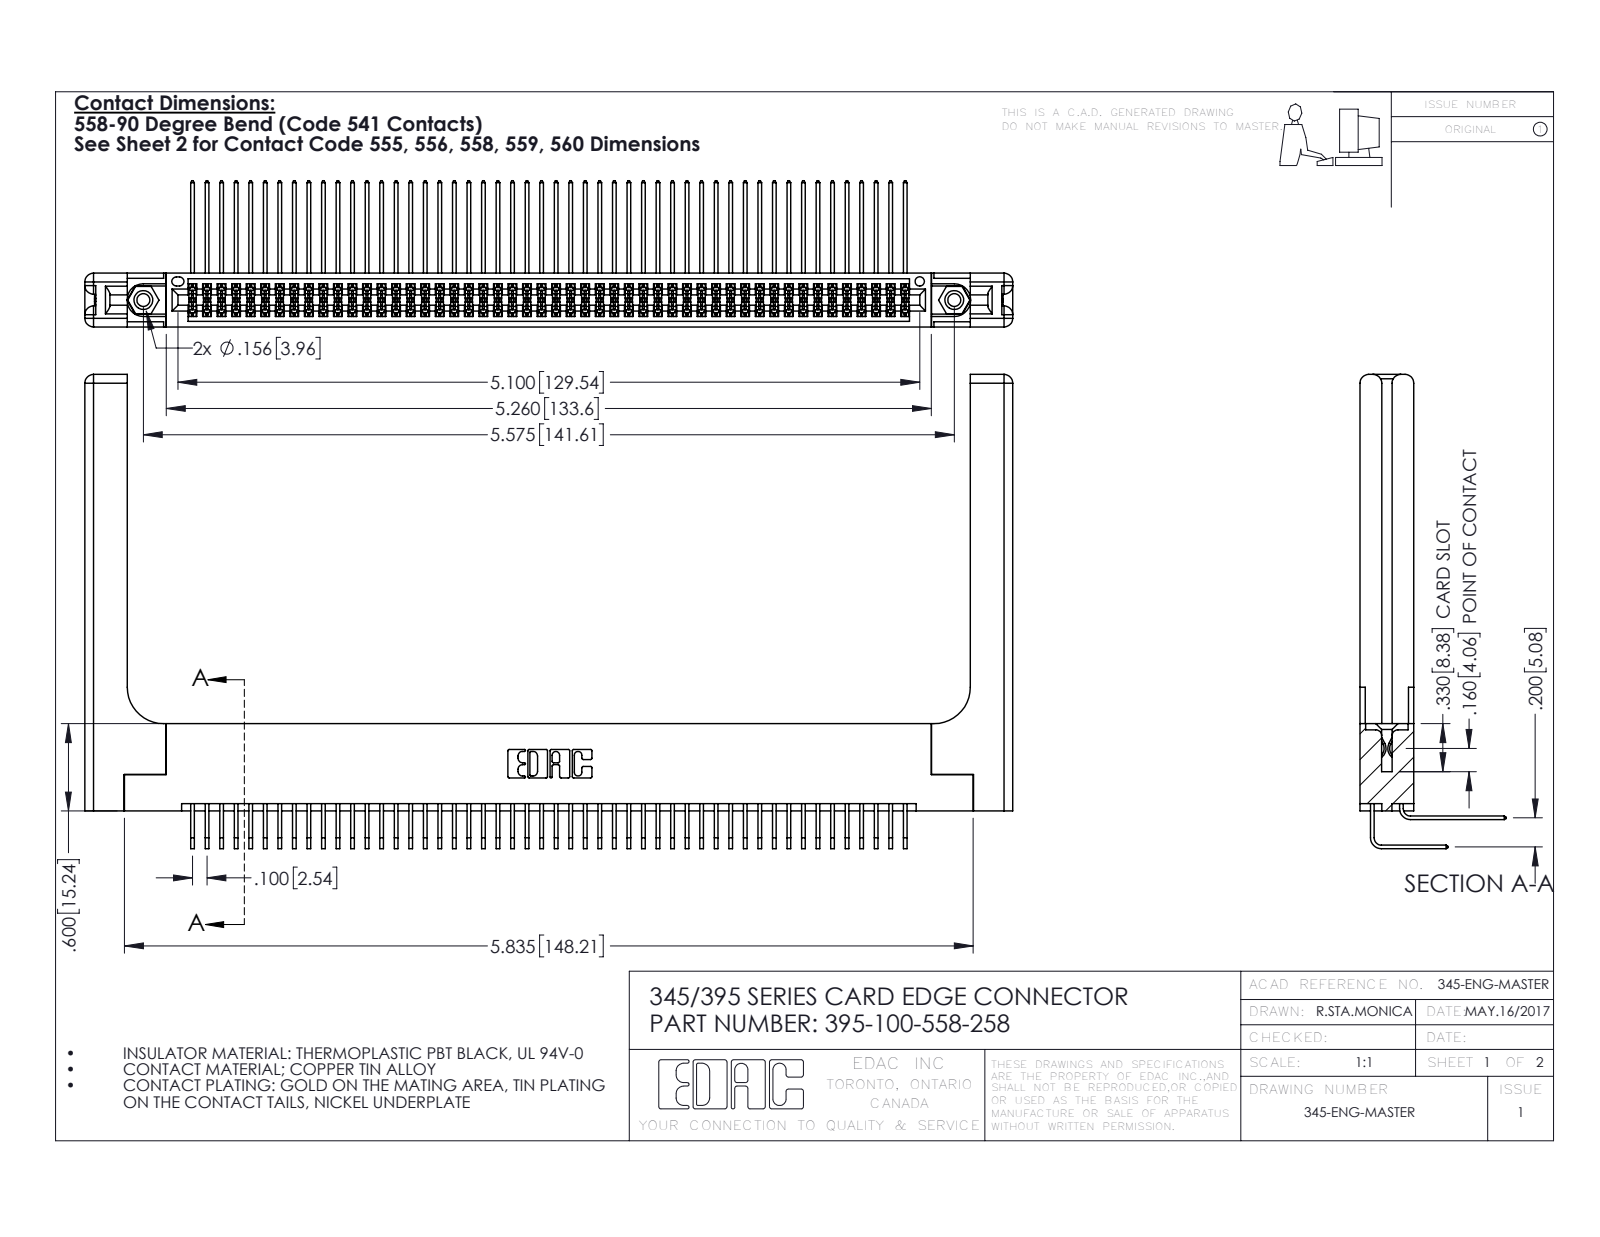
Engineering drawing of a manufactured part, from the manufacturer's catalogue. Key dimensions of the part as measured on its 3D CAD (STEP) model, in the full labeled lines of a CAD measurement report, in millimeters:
Part name (STEP PRODUCT): 345 Part_Flush Mounting Lugs - 0.156 Dia-TH; 345-292-001_558 559 Tail - 1; 345-220-058_345-220-058; 345-292-001_558 Tail - 2 (+2 more)
STEP written by: SolidWorks 2016 (CONFIG_CONTROL_DESIGN)
Units: millimetres
Bodies: 105 solids, 5582 faces (3728 planar, 1794 cylindrical, 60 other)
Overall size (bounding box): 162 × 82.8 × 25.5
Volume: 24 860 mm³ · Surface area: 32 150 mm²
Round holes (diameter × count): ⌀2.3 ×2, ⌀3.2 ×2, ⌀4 ×2, ⌀1.6 ×1
Round bosses / shafts (diameter × count): ⌀3.9 ×2
Partial cylindrical surfaces — rounded edges, fillets, slot ends (radius × count): R0.2 ×151, R0.3 ×22, R1.5 ×16, R0.2 ×6, R0.8 ×6, R0.7 ×3, R0.4 ×2, R0.5 ×2
Main face-to-face distances: 1.8, 7.6, 9.4, 5.1, 2.5, 6.9, 0.6, 5.7, 3.8, 3.8
Hole centre spacings: 6.9, 135.6, 141.6
